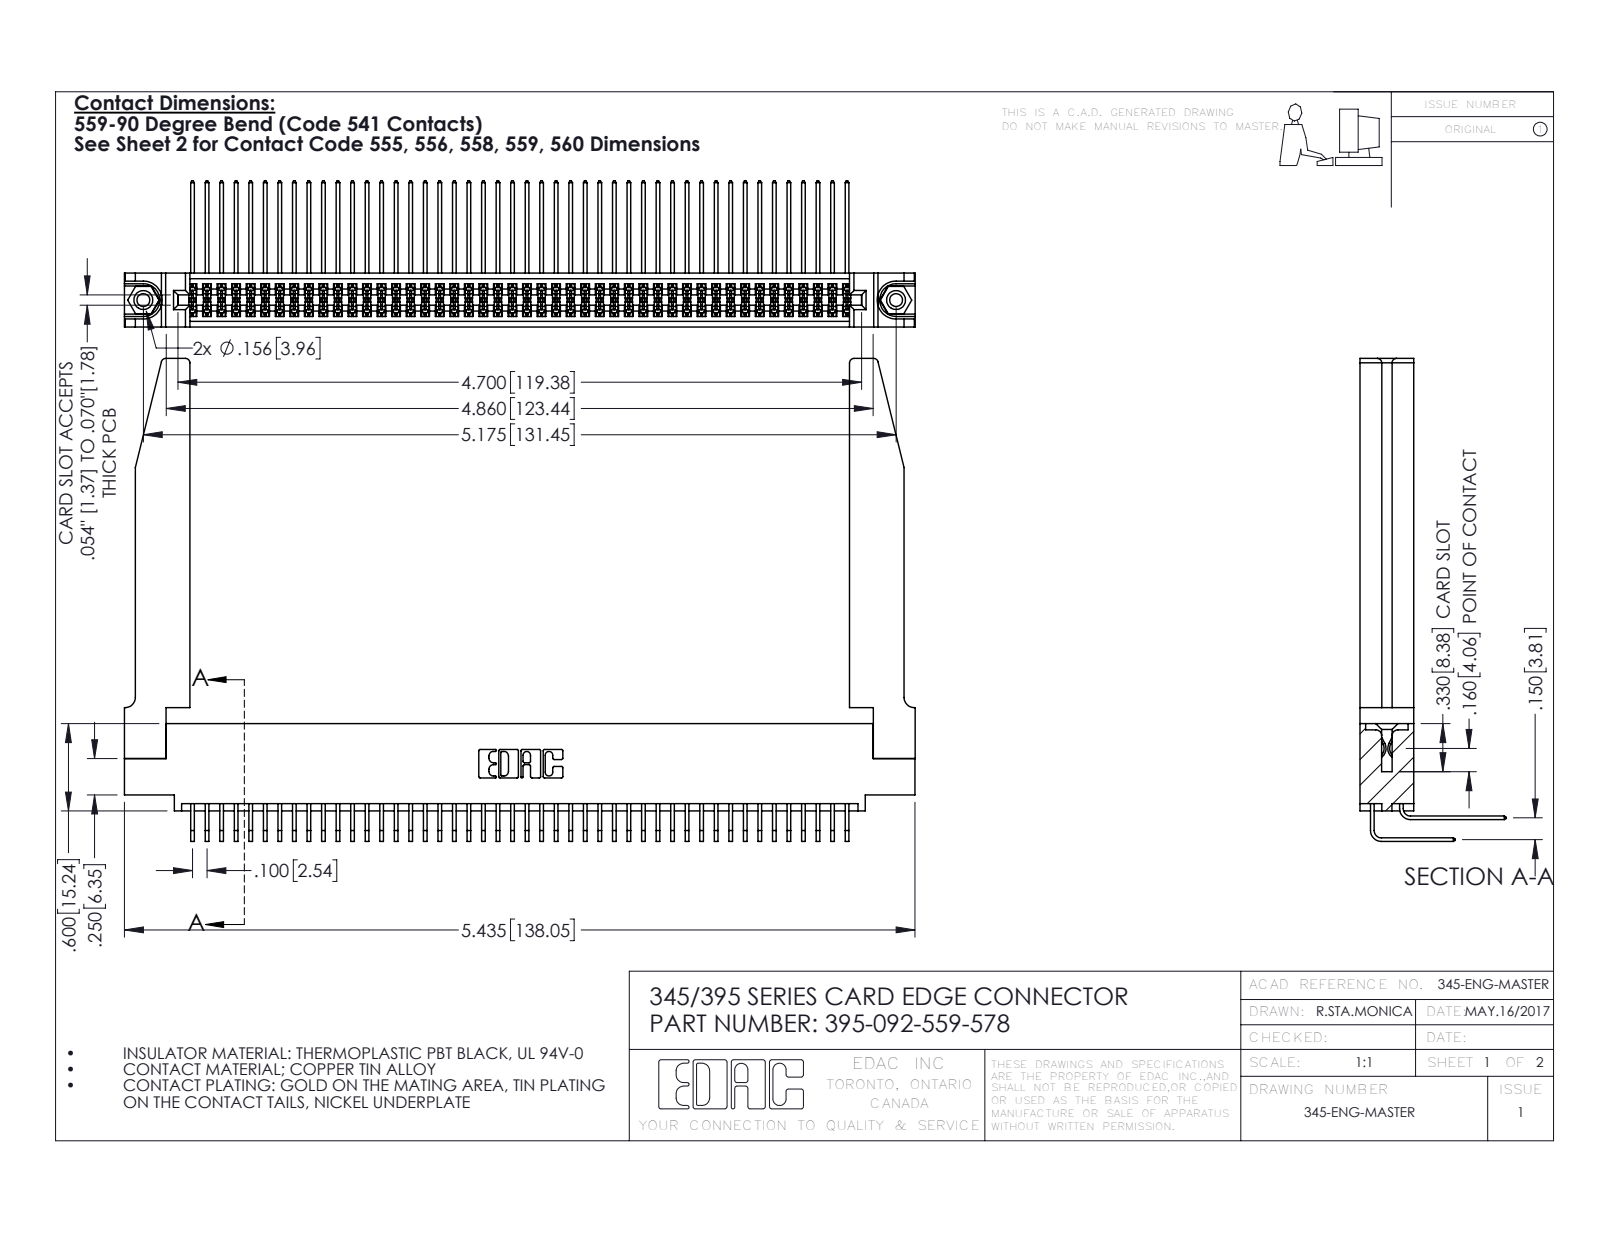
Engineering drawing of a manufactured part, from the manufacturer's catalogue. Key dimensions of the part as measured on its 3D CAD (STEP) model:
Part name (STEP PRODUCT): 345-220-078_345-220-078; 345-250-001_345-250-001-102; 345-292-001_558 559 Tail - 1; 395-092-559-578 (+2 more)
STEP written by: SolidWorks 2016 (CONFIG_CONTROL_DESIGN)
Units: inches
Bodies: 97 solids, 5148 faces (3446 planar, 1650 cylindrical, 52 other)
Overall size (bounding box): 5.436 × 3.319 × 1.005
Volume: 1.323 in³ · Surface area: 46.6 in²
Round holes (diameter × count): ⌀0.089 ×2, ⌀0.125 ×2, ⌀0.156 ×2, ⌀0.064 ×1
Round bosses / shafts (diameter × count): ⌀0.155 ×2
Partial cylindrical surfaces — rounded edges, fillets, slot ends (radius × count): R0.006 ×138, R0.01 ×22, R0.03 ×8, R0.007 ×6, R0.031 ×6, R0.026 ×3, R0.014 ×2, R0.019 ×2
Main face-to-face distances: 0.072, 0.37, 0.298, 0.2, 0.098, 0.272, 0.025, 0.225, 0.175, 0.15
Hole centre spacings: 0.27, 4.939, 5.175
